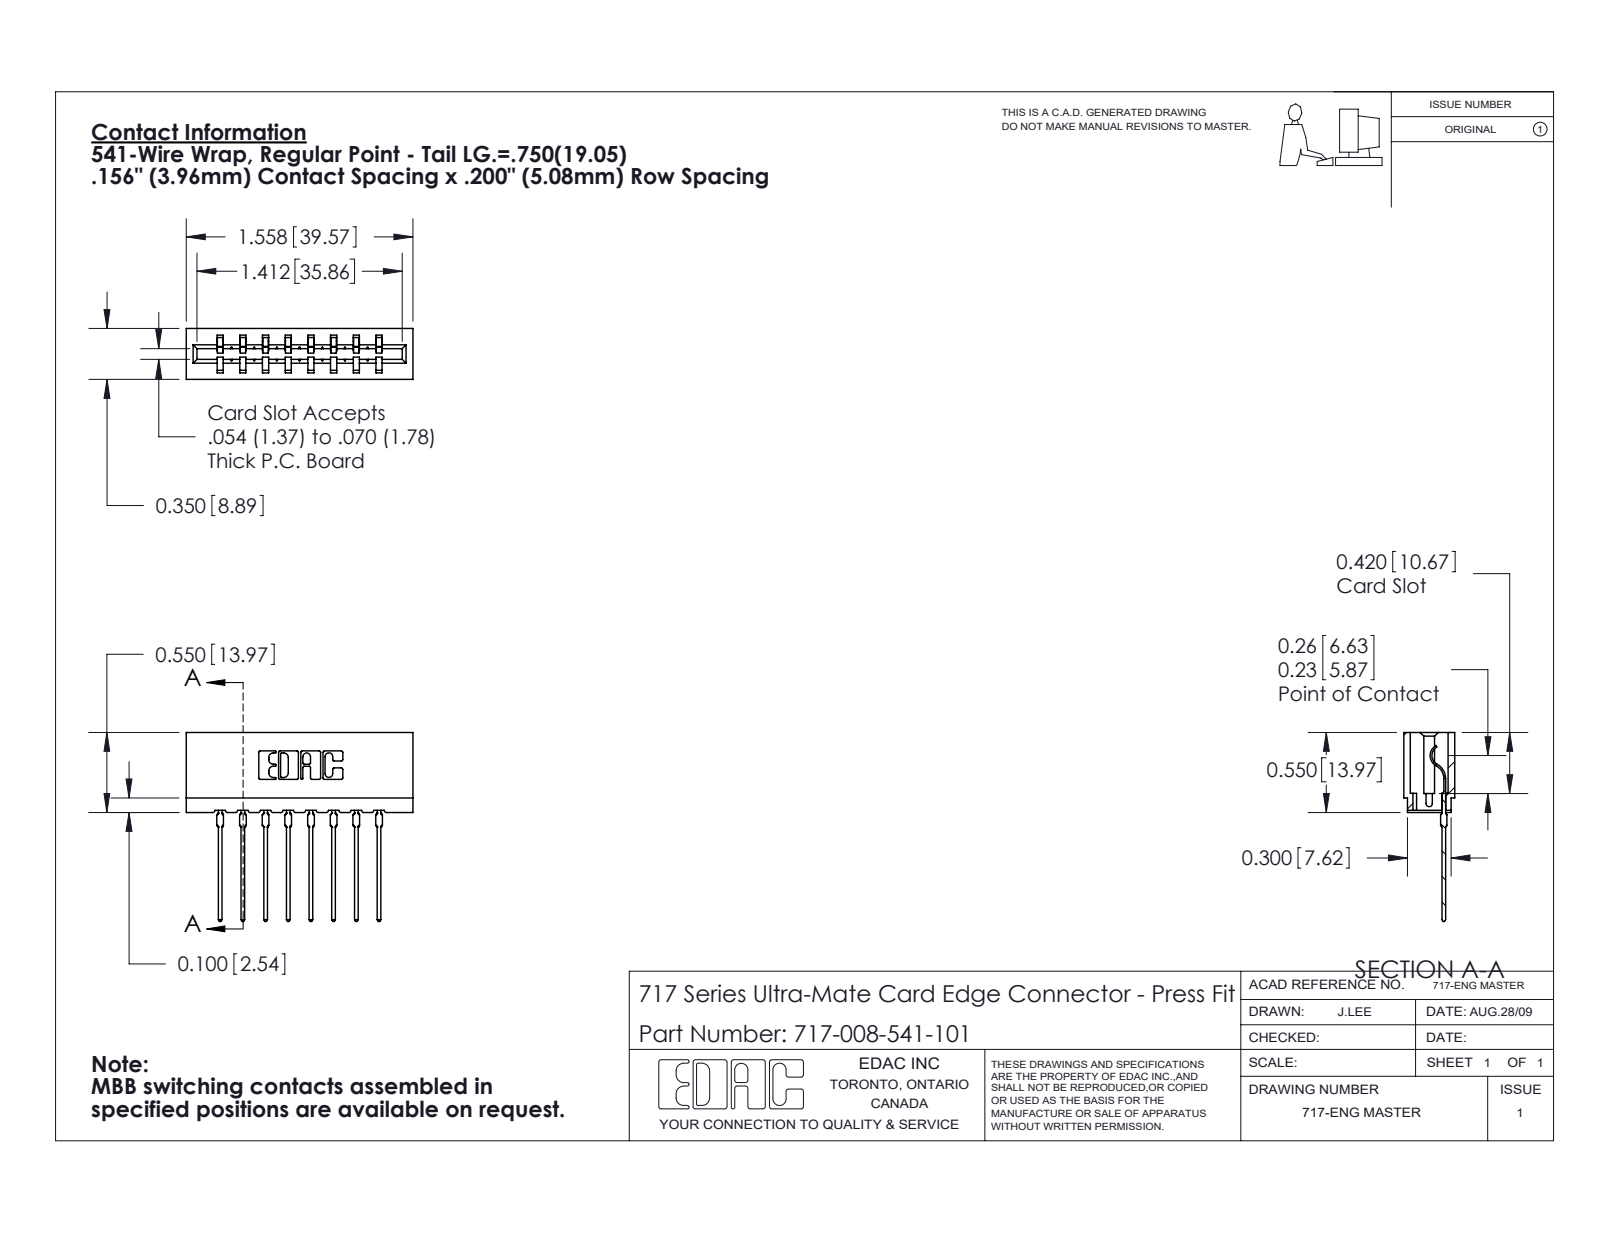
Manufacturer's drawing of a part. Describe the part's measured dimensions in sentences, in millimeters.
The part is named "717-008-541-101; 717 Part_Insulator Option - 06; 745-292-001_541". Its 3-D file was written by "SolidWorks 2020 (CONFIG_CONTROL_DESIGN)". It is 9 solids with 998 faces: 598 planar, 192 cylindrical and 208 other. Overall it measures 39.6 by 33 by 8.9 millimeters. Its volume is 3 520 cubic millimeters and its surface area 4 757 square millimeters. Partial cylindrical surfaces (rounded edges, fillets, slot ends): 22 of radius 0.3, 16 of radius 0.4, 16 of radius 0.5, 6 of radius 0.2, 6 of radius 0.8, 4 of radius 0.1, 4 of radius 0.3, 3 of radius 0.7. The main face-to-face distances are 5.4, 4, 3.5, 15.8, 11.9, 5, 7.9, 8.9, 1.1, 6.9.
